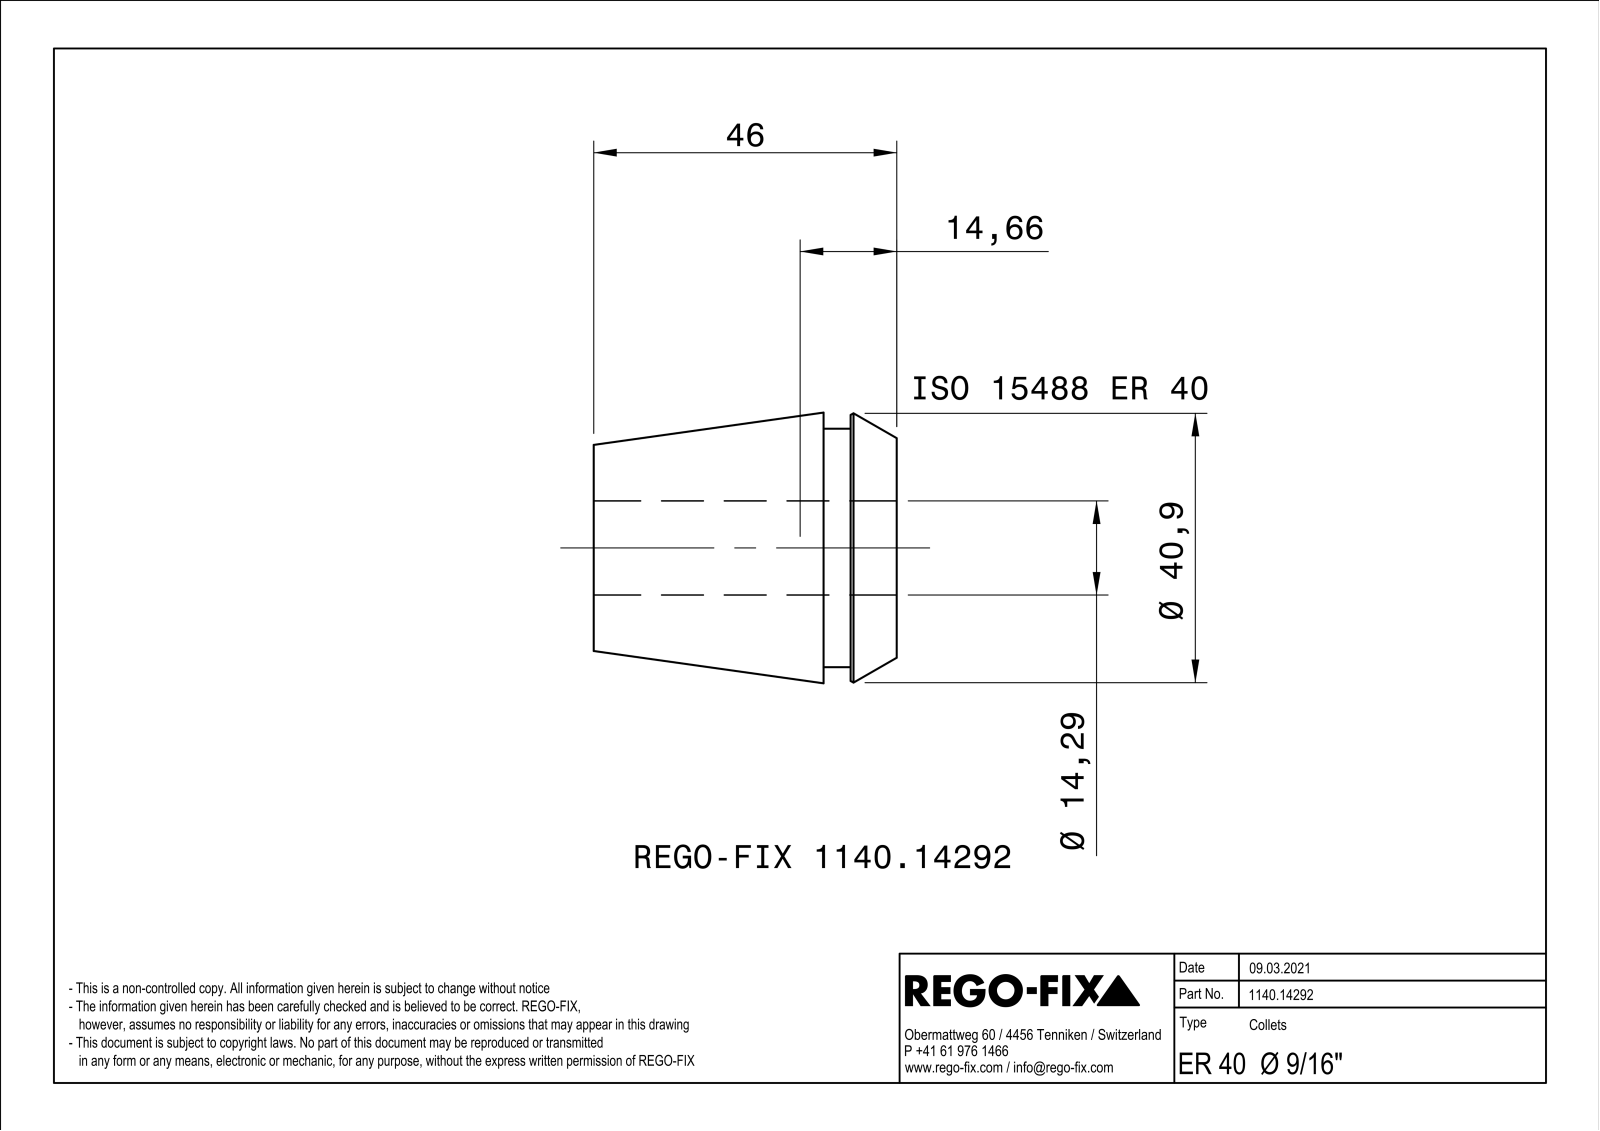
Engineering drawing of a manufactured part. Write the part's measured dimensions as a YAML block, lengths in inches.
part_name: "NOCUT"
step_written_by: "SIEMENS PLM Software Solid Edge ST10 (AUTOMOTIVE_DESIGN)"
units: inches
bodies: {solids: 1, faces: 177, planar: 88, cylindrical: 9, other: 80}
overall_size: [1.811, 1.614, 1.614]
volume: 2.032
surface_area: 34.53
round_holes:
  - {diameter: 0.563, count: 1}
round_bosses_or_shafts:
  - {diameter: 1.425, count: 1}
face_to_face_distances: [0.039, 1.811, 0.437, 1.374, 0.276, 0.161, 1.535, 0.295, 0.02, 0.142]
